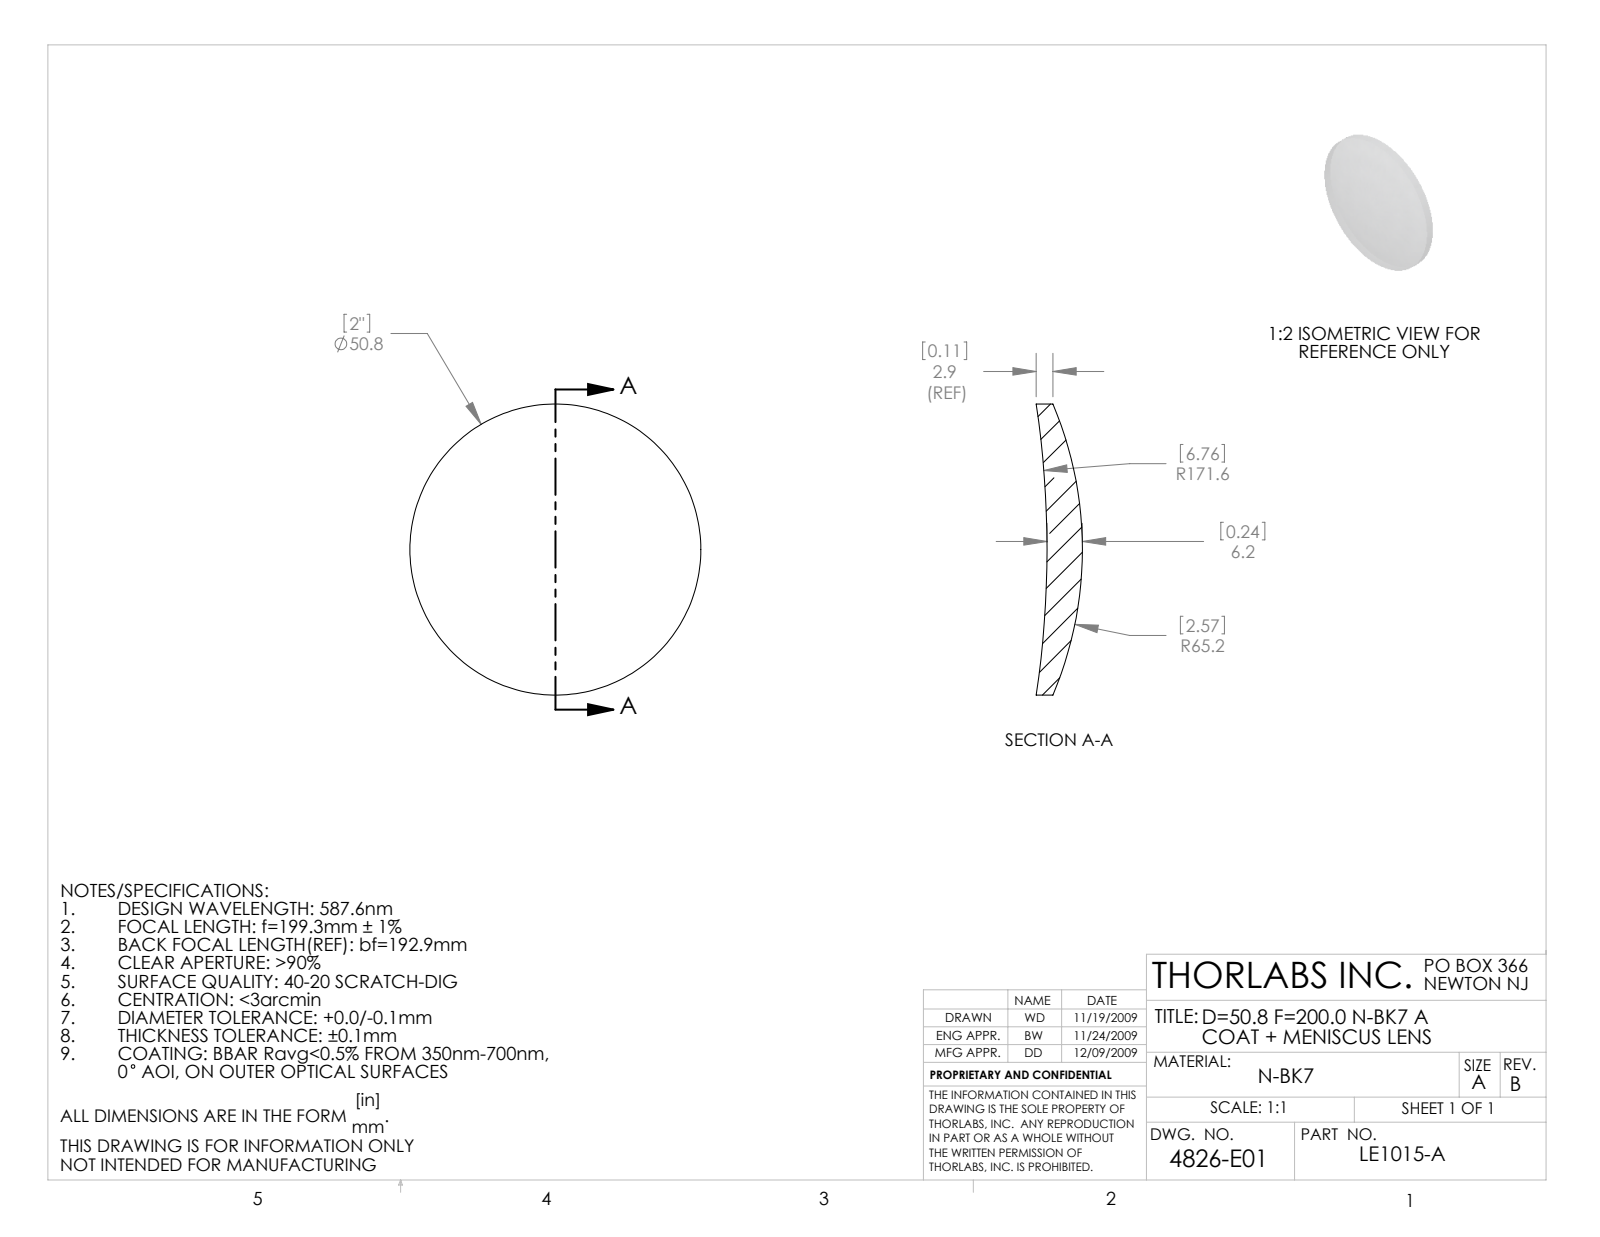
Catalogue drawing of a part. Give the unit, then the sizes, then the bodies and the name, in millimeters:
Units: millimetres
Overall size (bounding box): 50.8 × 50.8 × 8.07
Round bosses / shafts (diameter × count): ⌀50.8 ×1
Volume: 9 286 mm³ · Surface area: 4 614 mm²
Bodies: 1 solid, 6 faces (0 planar, 2 cylindrical, 4 other)
Part name (STEP PRODUCT): 4826-E0W
STEP written by: SolidWorks 2009 (AUTOMOTIVE_DESIGN)
